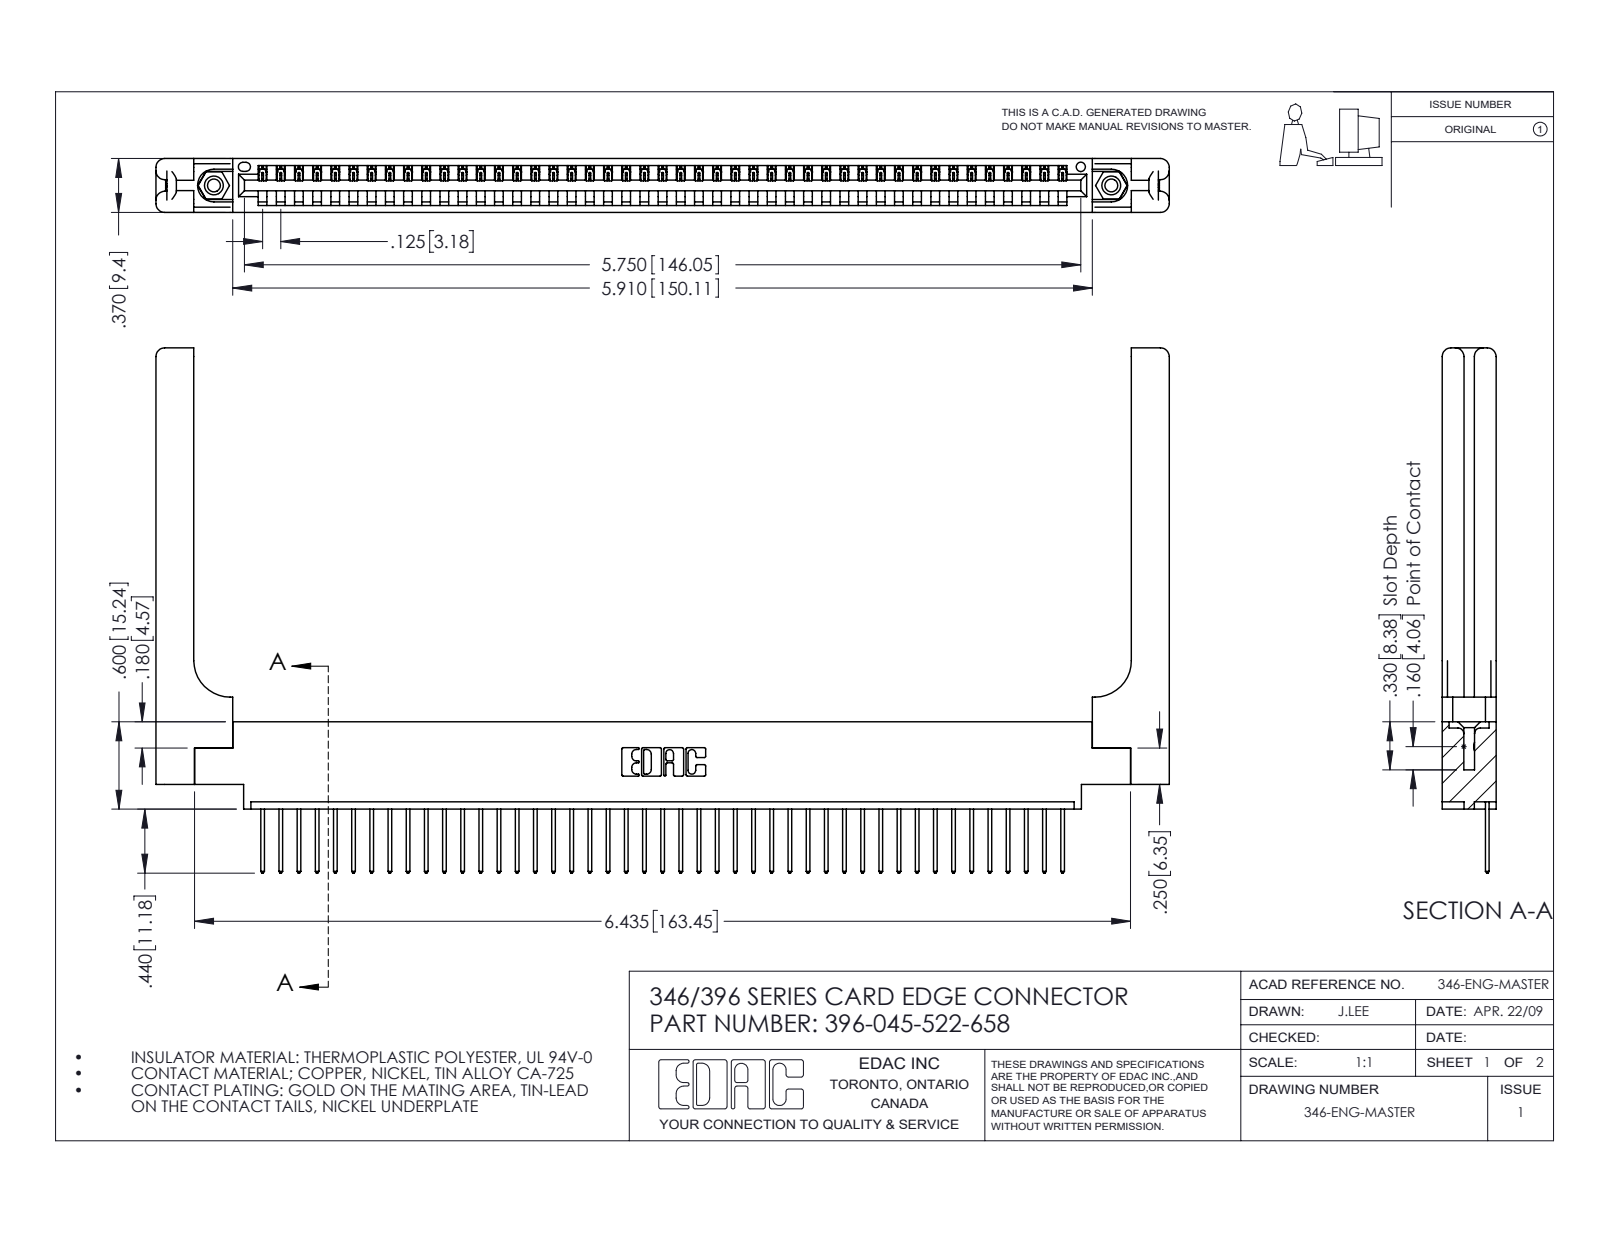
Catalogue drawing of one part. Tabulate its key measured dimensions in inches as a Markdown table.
| quantity | value |
| --- | --- |
| part name | 345-250-001_345-250-001-102; 396-045-522-658; 345-292-001_345-293-122; 346 Part_0.170 Offset - 0.156 Dia-TH (+1 more) |
| STEP written by | SolidWorks 2016 (CONFIG_CONTROL_DESIGN) |
| units | inches |
| bodies | 50 solids, 2992 faces (2028 planar, 904 cylindrical, 60 other) |
| overall size | 6.966 × 3.61 × 0.37 |
| volume | 1.485 in³ |
| surface area | 41.13 in² |
| round holes (diameter × count) | 0.089 × 2, 0.125 × 2, 0.156 × 2, 0.064 × 1 |
| round bosses / shafts (diameter × count) | 0.155 × 2 |
| partial cylindrical surfaces (radius × count) | 0.006 × 90, 0.01 × 90, 0.01 × 22, 0.06 × 16, 0.007 × 6, 0.031 × 6, 0.026 × 3, 0.03 × 2 |
| main face-to-face distances | 0.37, 0.048, 0.322, 0.072, 0.148, 0.15, 0.25, 0.298, 0.025, 0.222 |
| hole center spacings | 0.246, 5.961, 6.17 |
